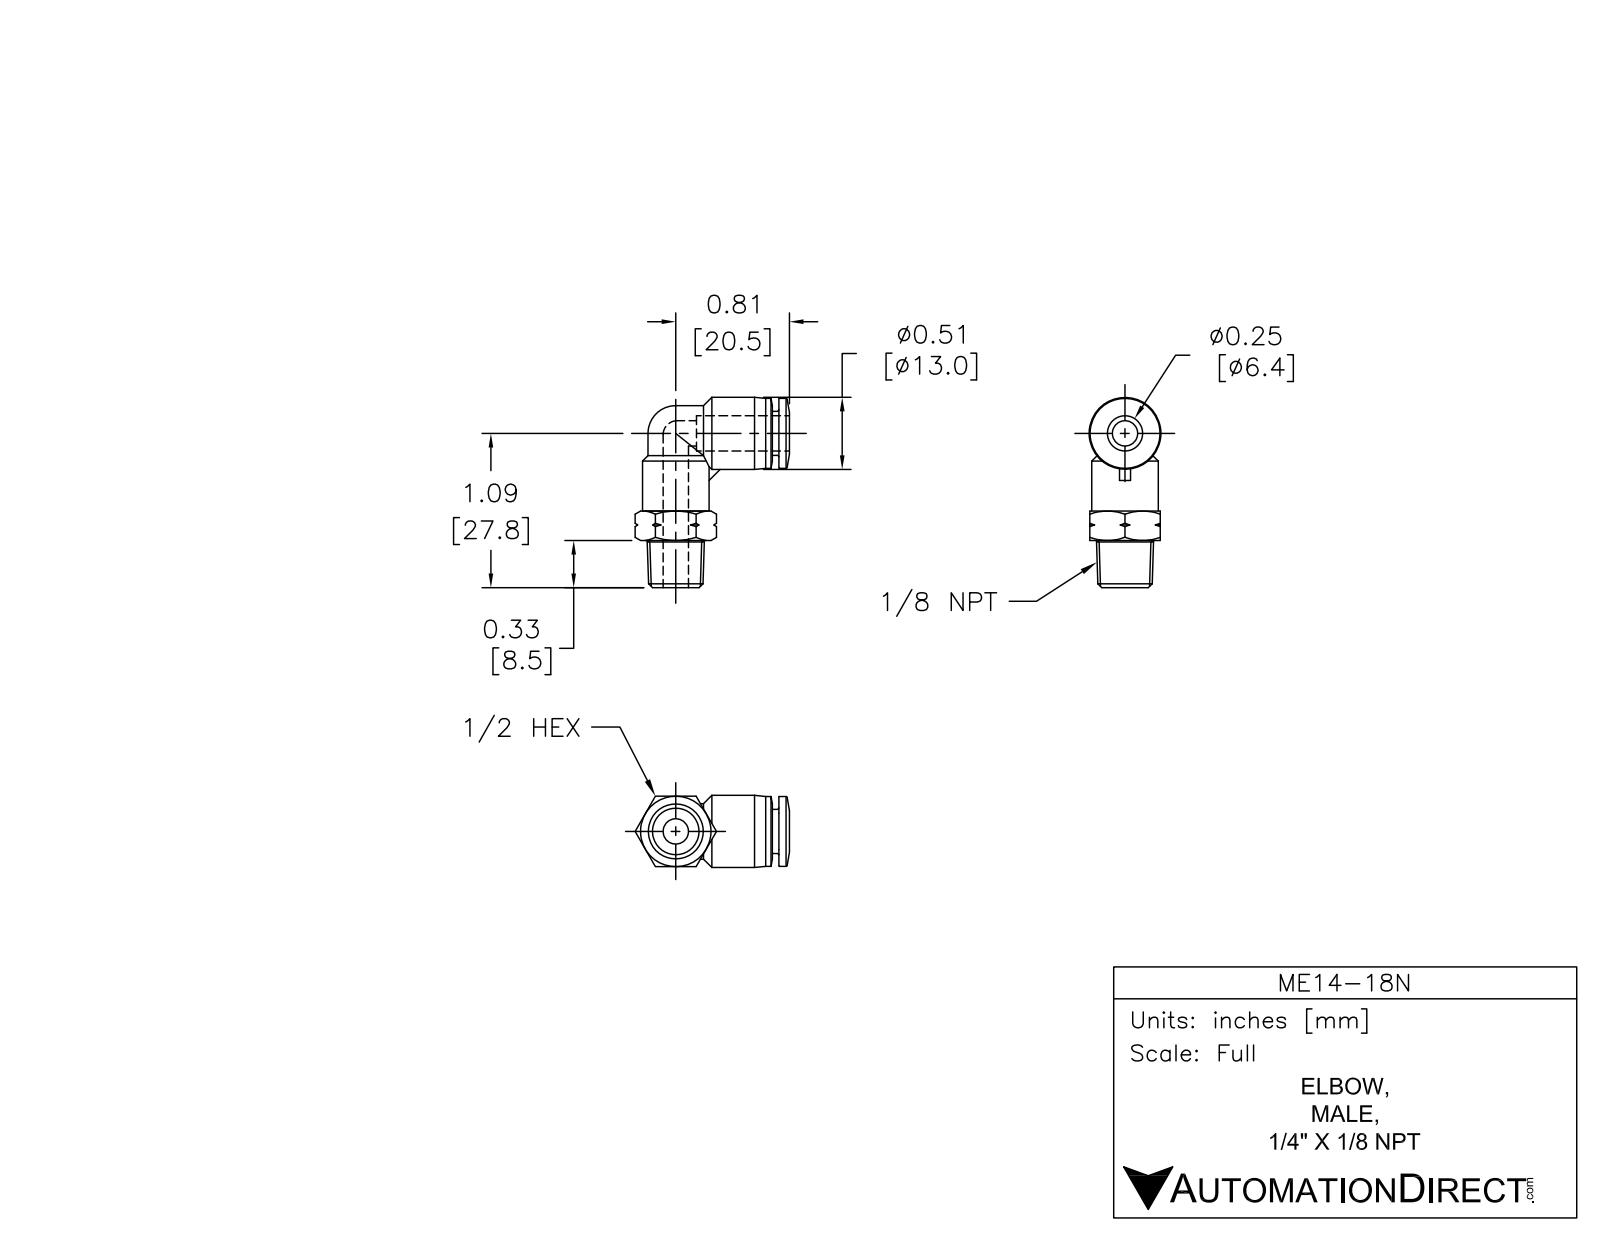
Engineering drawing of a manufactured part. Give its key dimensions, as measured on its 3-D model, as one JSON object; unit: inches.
{"part_name": "ME14-18N", "step_written_by": "SolidWorks 2015 (AUTOMOTIVE_DESIGN)", "units": "inches", "bodies": {"solids": 1, "faces": 84, "planar": 15, "cylindrical": 20, "other": 49}, "overall_size": [1.35, 1.096, 0.512], "volume_in3": 0.243, "surface_area_in2": 4.483, "round_holes": [[0.177, 2], [0.258, 1]], "round_bosses_or_shafts": [[0.394, 2], [0.512, 1], [0.496, 1], [0.472, 1], [0.313, 1]], "face_to_face_distances": [0.5, 0.335, 0.047, 0.539, 0.587, 0.543, 0.209, 0.211, 0.289, 0.079]}
